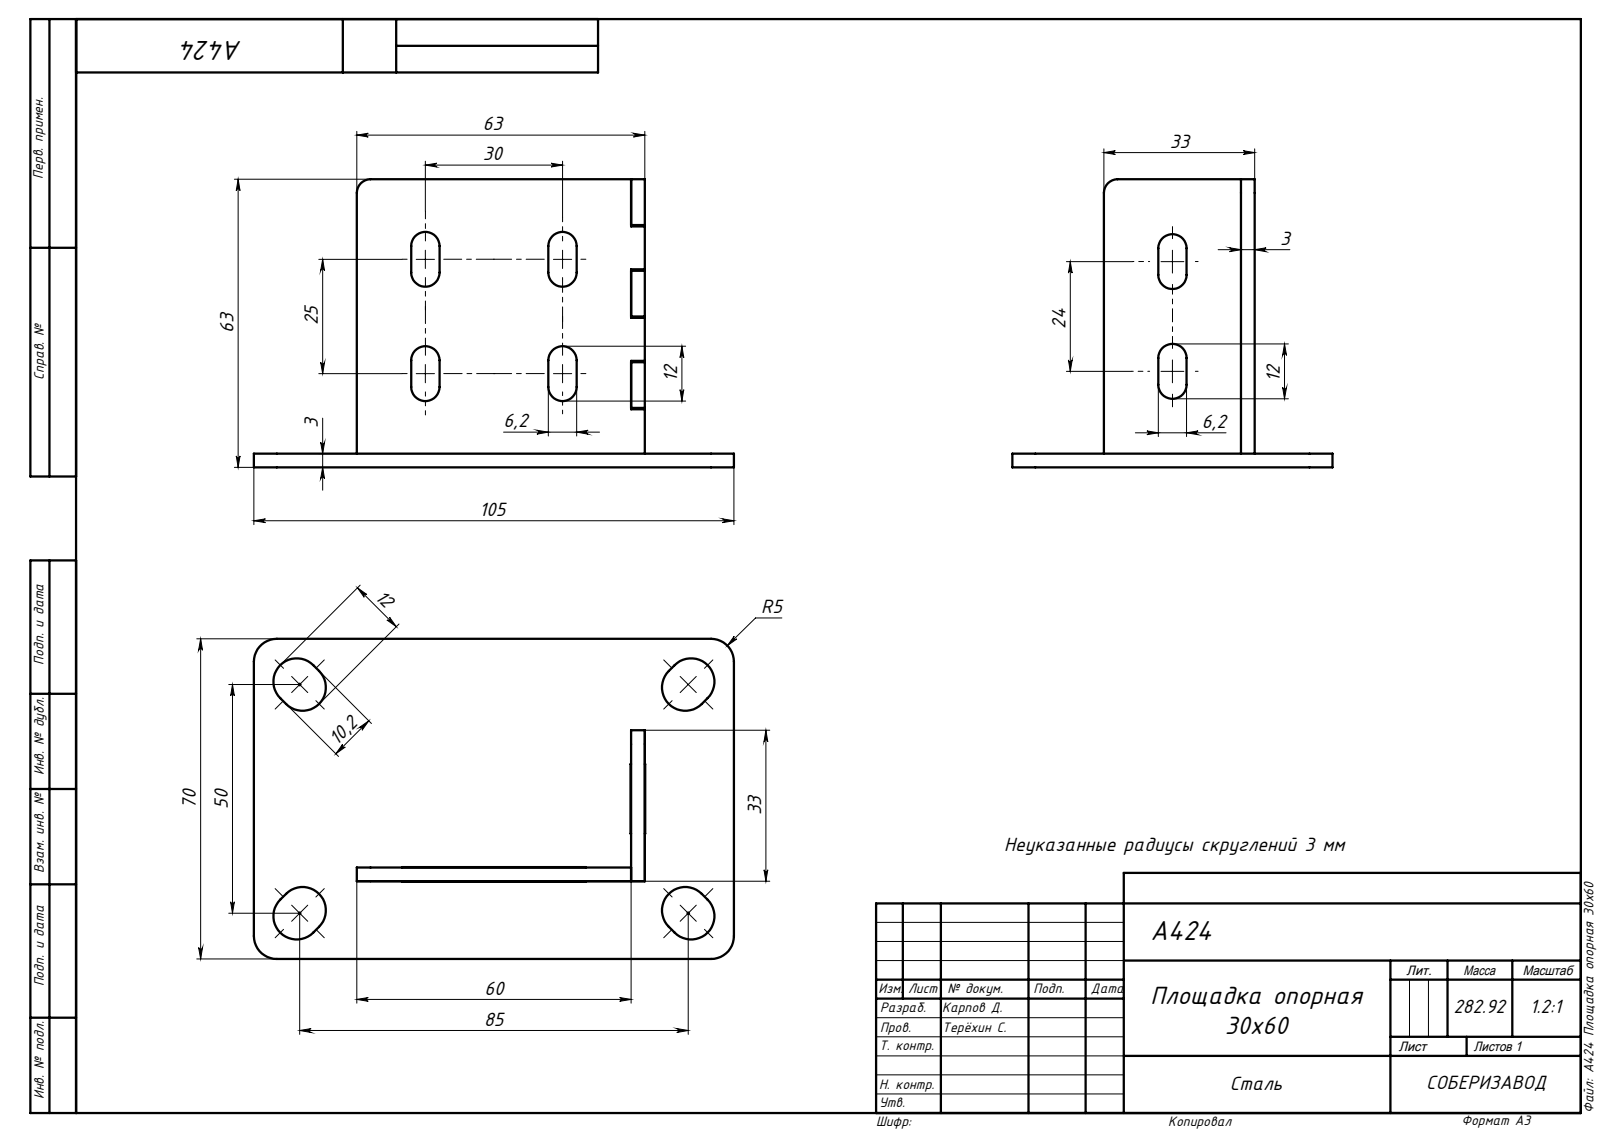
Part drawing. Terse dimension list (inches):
name: A424 Основание_00; A424 Площадка опорная 30х60; A424 Боковина с пазом 2_00; A424 Боковина с пазом 1_00
written by: SolidWorks 2020 (AUTOMOTIVE_DESIGN)
unit: in
bodies: 3 solids, 108 faces (74 planar, 34 cylindrical, 0 other)
size: 4.134 × 2.756 × 2.48
volume: 2.213 in³; area: 43.34 in²
rounds: 12× R0.122, 8× R0.201, 4× R0.197, 2× R0.118
face distances: 0.118, 0.787, 1.969, 2.48, 2.362, 0.886, 3.248, 0.122, 2.087, 0.669
